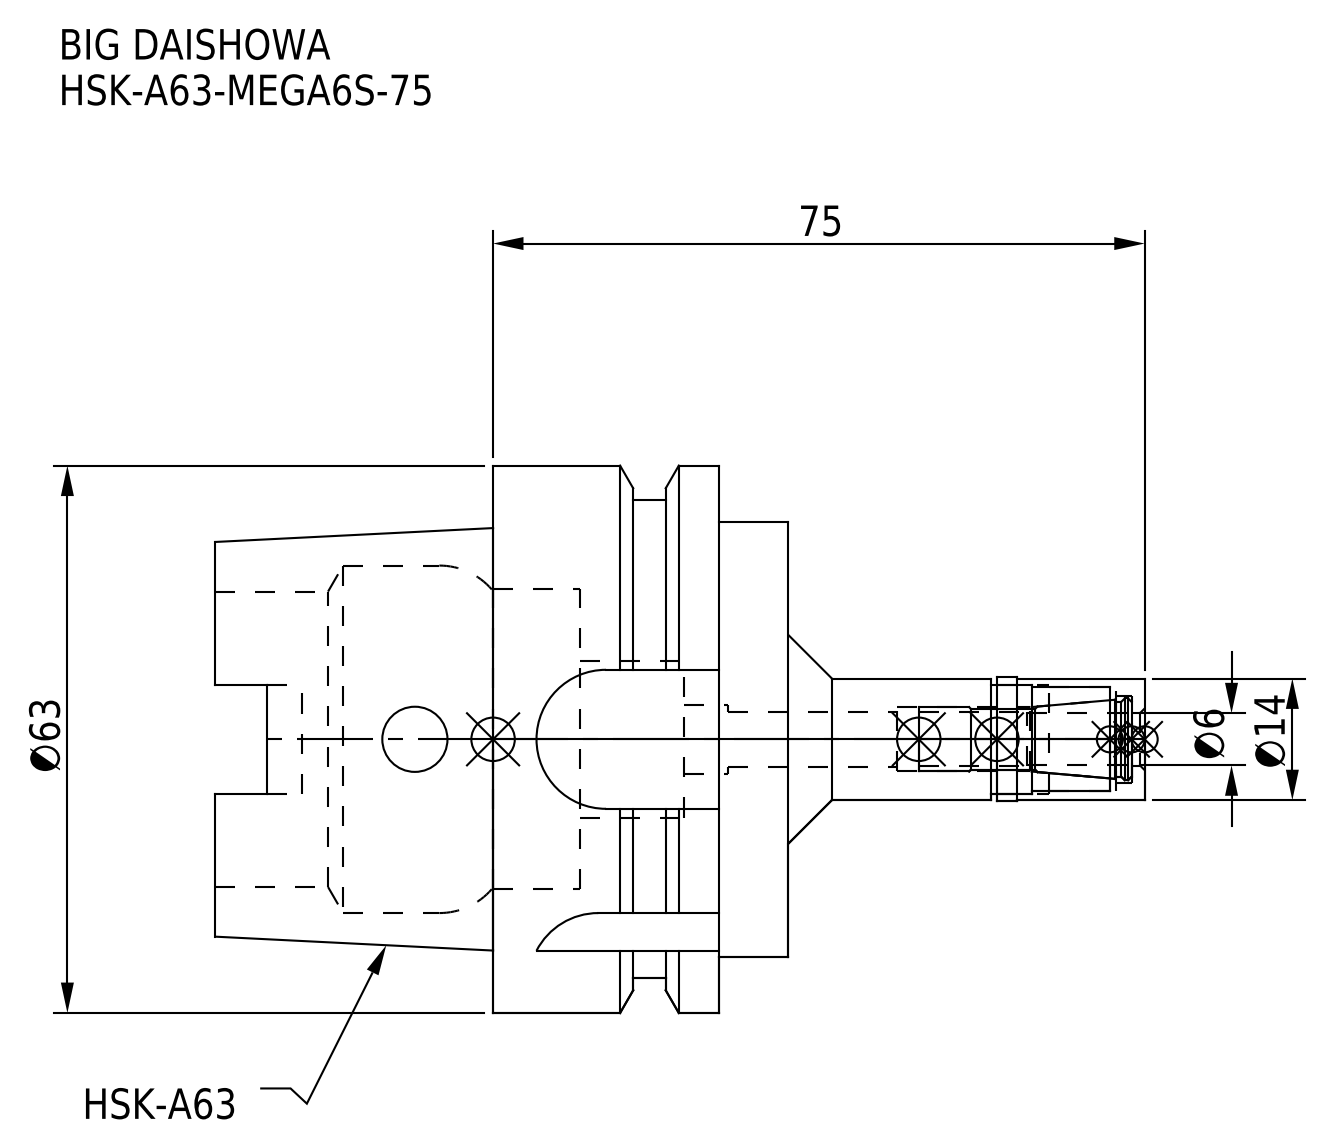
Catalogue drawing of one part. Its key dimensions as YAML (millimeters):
part_name: "HA63MS06075-060_ASM.stp; HSK-A63-MEGA6S-75-060.stp; HSK-A63-MEGA6S-75; MGN6S_1.stp (+3 more)"
step_written_by: "SolidWorks 2019 (CONFIG_CONTROL_DESIGN)"
units: millimeters
bodies: {solids: 2, faces: 122, planar: 47, cylindrical: 55, other: 20}
overall_size: [107, 63, 63]
volume: 102204
surface_area: 27655
round_holes:
  - {diameter: 6.1, count: 1}
  - {diameter: 6.4, count: 1}
  - {diameter: 7.4, count: 1}
  - {diameter: 7.5, count: 1}
  - {diameter: 8, count: 1}
  - {diameter: 10, count: 1}
  - {diameter: 12, count: 1}
  - {diameter: 12.5, count: 1}
  - {diameter: 18, count: 1}
  - {diameter: 34, count: 1}
  - {diameter: 34.5, count: 1}
  - {diameter: 40, count: 1}
round_bosses_or_shafts:
  - {diameter: 63, count: 1}
  - {diameter: 55, count: 1}
  - {diameter: 50, count: 1}
  - {diameter: 14.3, count: 1}
  - {diameter: 14, count: 1}
partial_cylinders:
  - {radius: 2.88, count: 4}
  - {radius: 8, count: 4}
face_to_face_distances: [34, 26, 8, 24.05, 16.05, 9.95, 32, 58, 66, 41.95]
